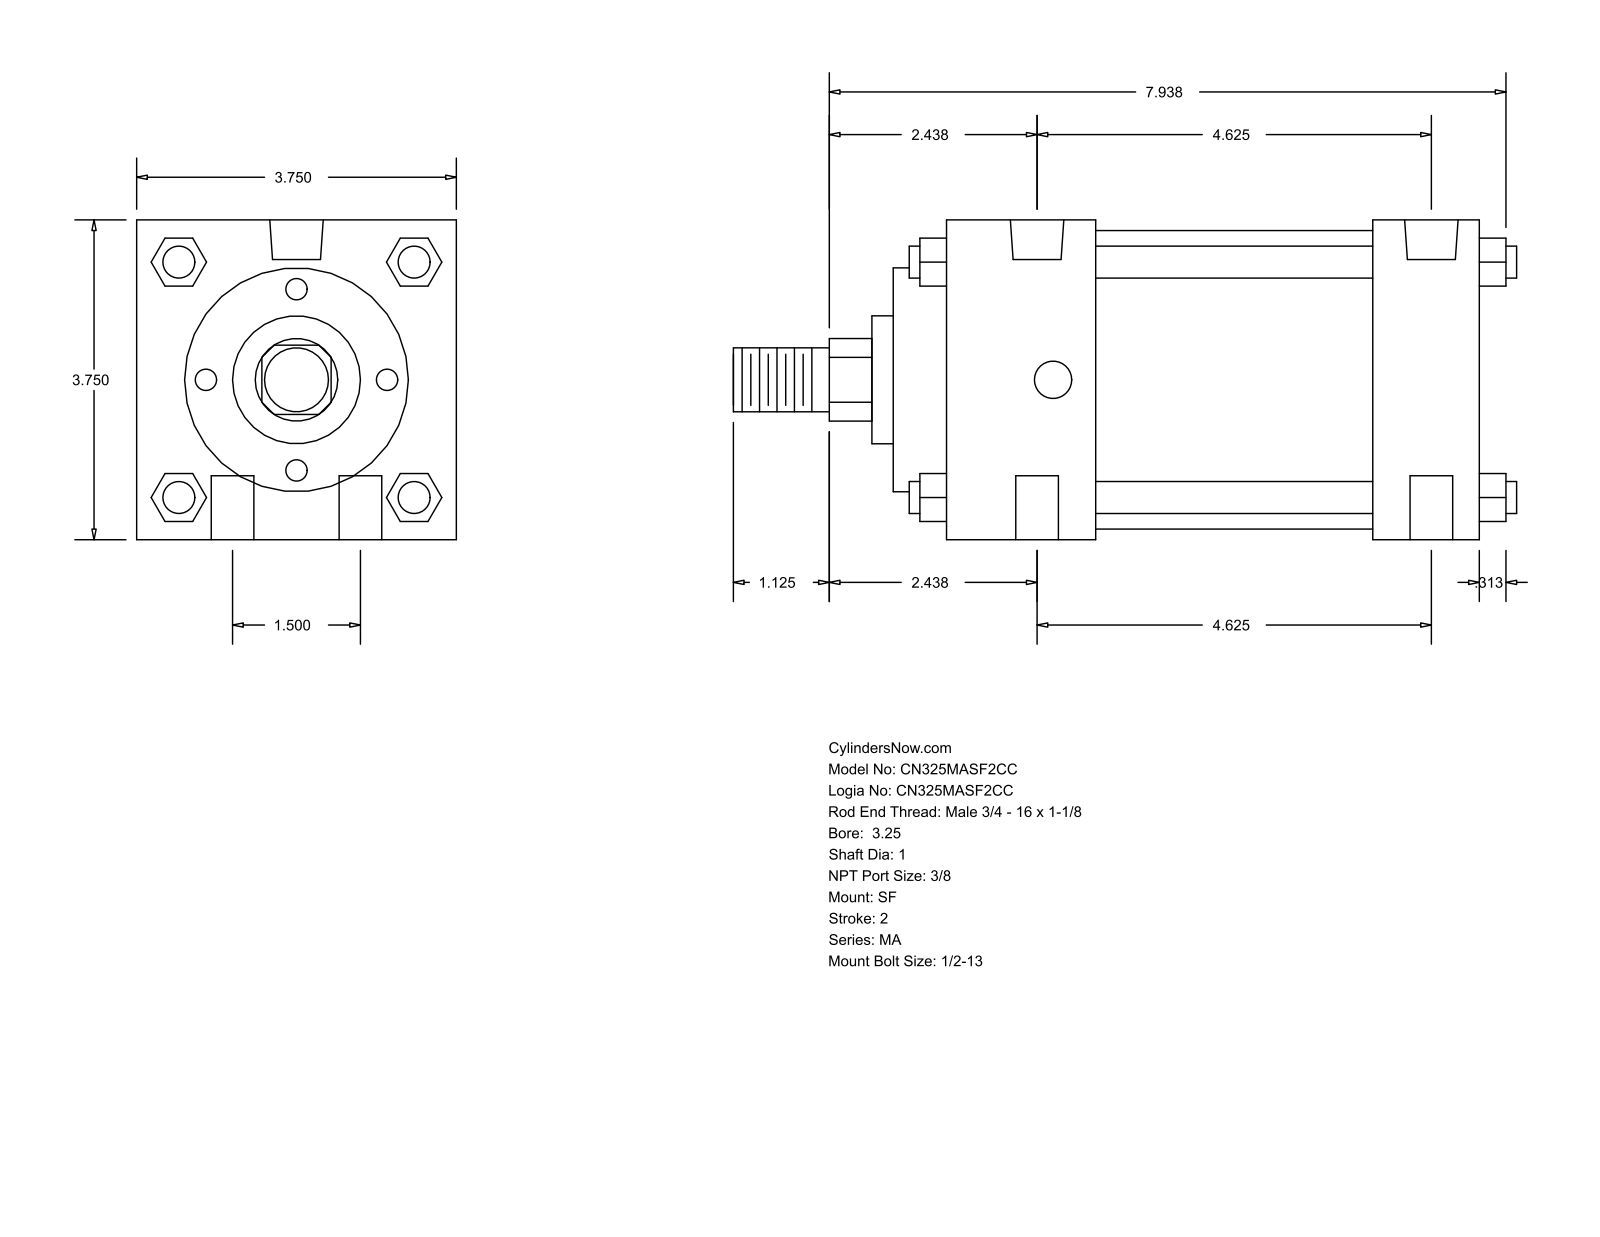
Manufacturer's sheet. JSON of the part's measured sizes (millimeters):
{"part_name": "MA_SF__0325_1", "step_written_by": "GSSL Pune (CONFIG_CONTROL_DESIGN)", "units": "millimeters", "bodies": {"solids": 0, "faces": 126, "planar": 95, "cylindrical": 31, "other": 0}, "overall_size": [233.36, 95.25, 95.25], "round_holes": [[12.7, 4], [11.11, 2], [15.93, 2]], "round_bosses_or_shafts": [[9.53, 4], [88.9, 1], [66.67, 1], [38.1, 1], [25.4, 1], [19.05, 1]], "partial_cylinders_radius": [[12.29, 1]], "face_to_face_distances": [95.24, 158.76, 127.01, 31.75, 44.46, 82.55, 114.3, 15.87, 60.33, 142.88], "hole_center_spacings": [19.05, 119.01, 117.48, 38.1, 123.5, 107.95]}
